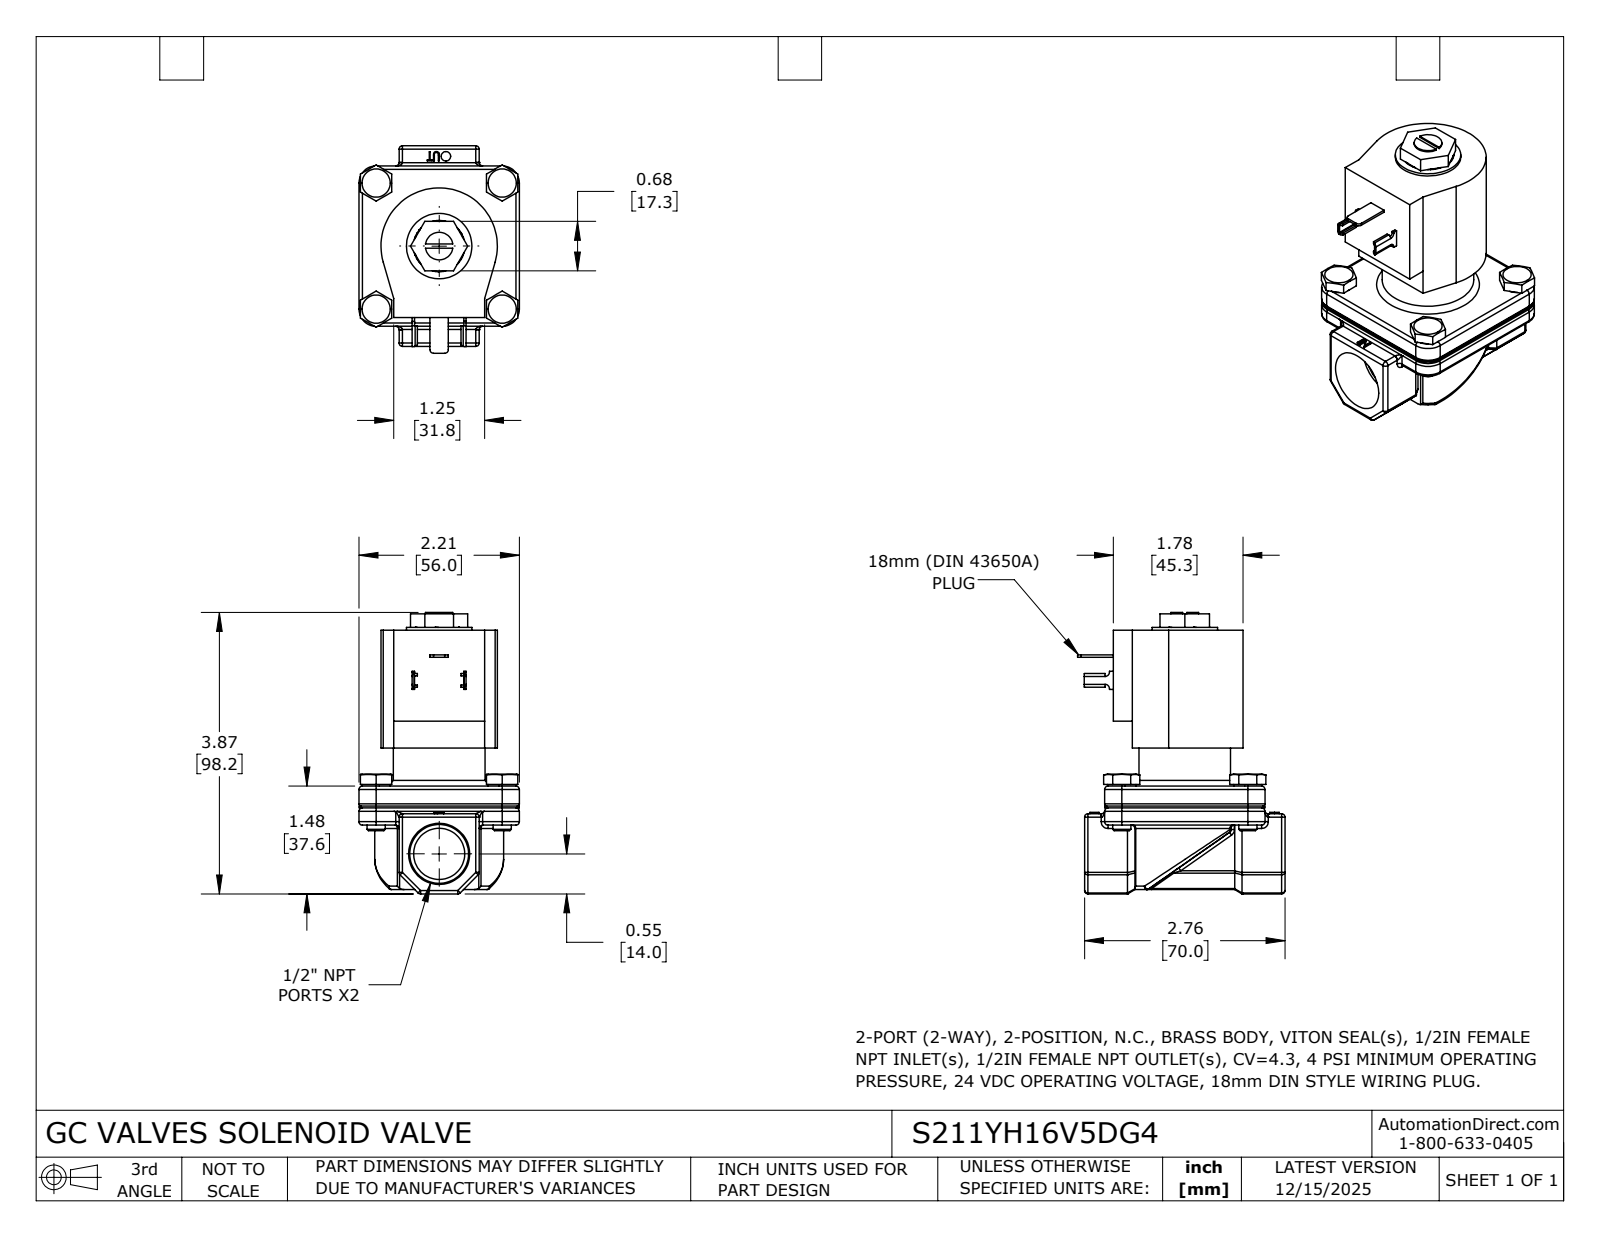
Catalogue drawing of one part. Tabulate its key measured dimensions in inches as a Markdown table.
| quantity | value |
| --- | --- |
| part name | S211YH16V5DG4 |
| STEP written by | SolidWorks 2024 (CONFIG_CONTROL_DESIGN) |
| units | inches |
| bodies | 1 solid, 507 faces (201 planar, 158 cylindrical, 148 other) |
| overall size | 3.867 × 2.851 × 2.205 |
| volume | 9.426 in³ |
| surface area | 42.83 in² |
| round holes (diameter × count) | 0.703 × 1, 0.706 × 1 |
| round bosses / shafts (diameter × count) | 0.388 × 4, 0.25 × 4, 1.26 × 1, 0.9 × 1, 0.464 × 1, 0.38 × 1 |
| partial cylindrical surfaces (radius × count) | 0.047 × 64, 0.006 × 4, 0.031 × 4, 0.041 × 4, 0.234 × 4, 0.236 × 4, 0.05 × 2, 0.06 × 2 |
| main face-to-face distances | 2.143, 0.059, 0.551, 1.654, 0.537, 2.68, 2.205, 1.06, 0.523, 1.62 |
